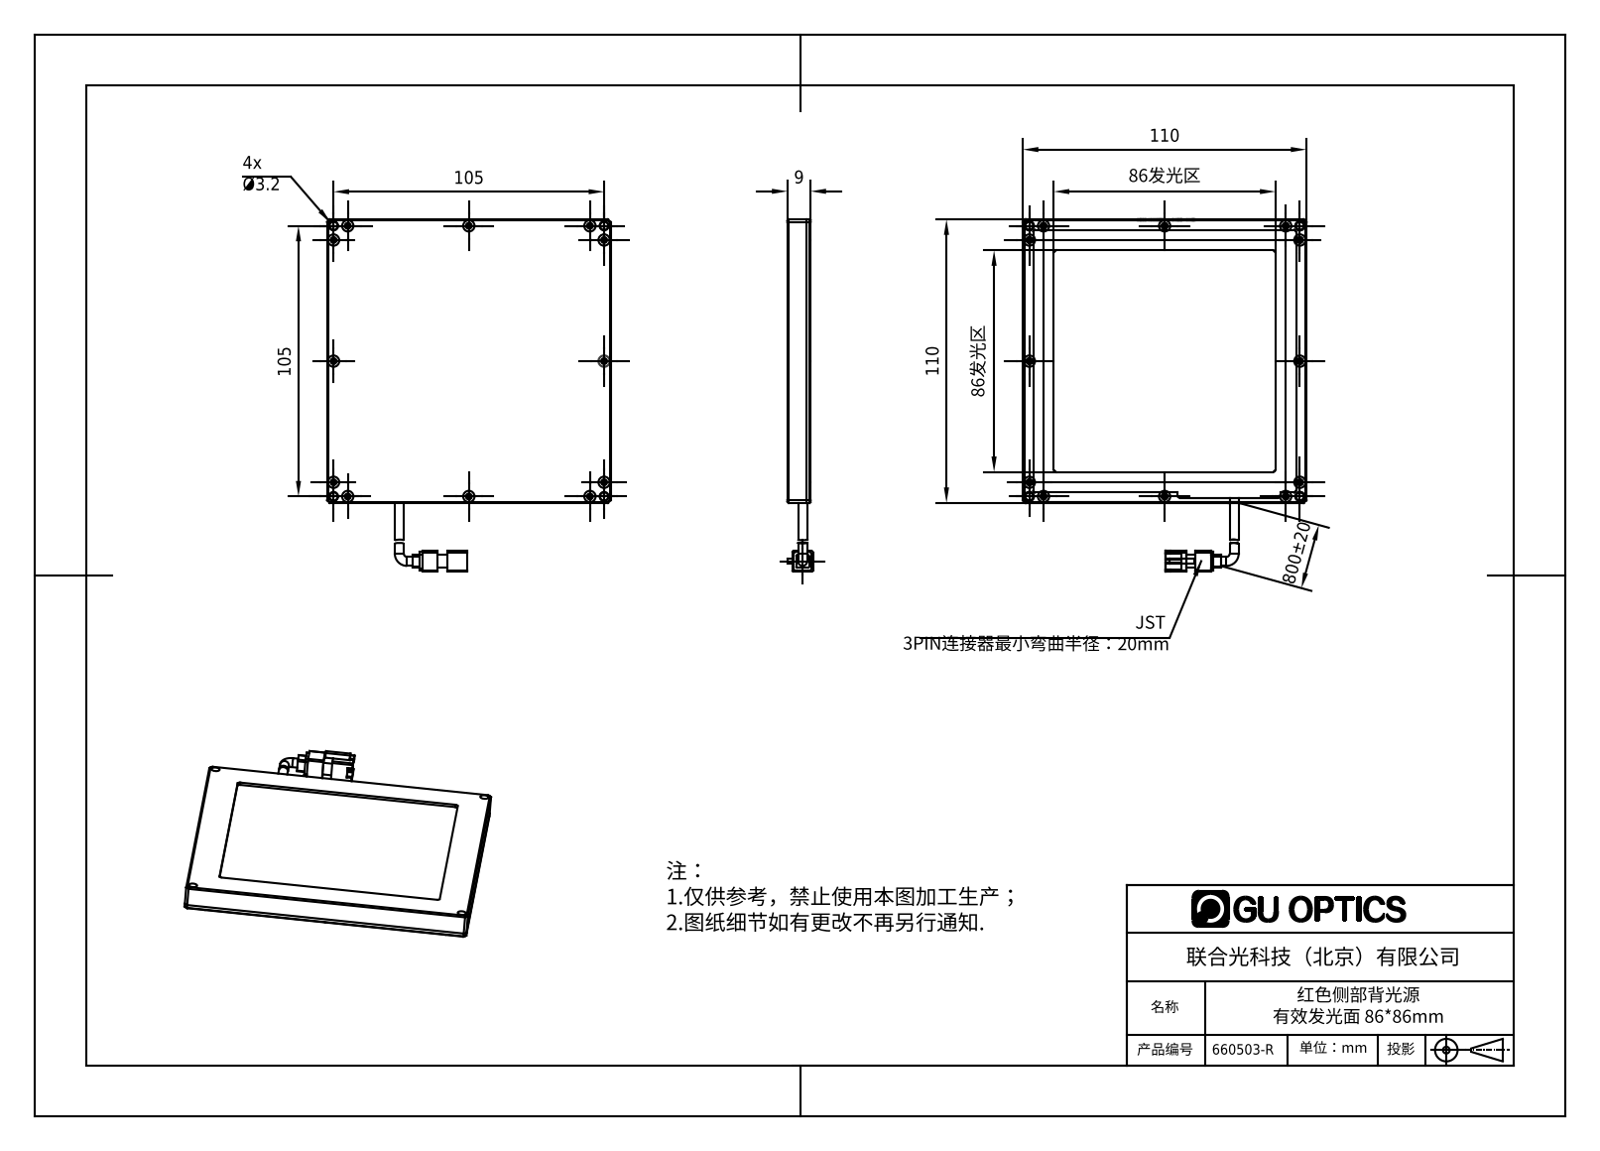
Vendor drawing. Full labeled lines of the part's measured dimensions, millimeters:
Part name (STEP PRODUCT): 660503-R
STEP written by: SolidWorks 2016 (AUTOMOTIVE_DESIGN)
Units: millimetres
Bodies: 5 solids, 415 faces (184 planar, 121 cylindrical, 110 other)
Overall size (bounding box): 136.69 × 110 × 10
Volume: 69 130 mm³ · Surface area: 61 430 mm²
Round holes (diameter × count): ⌀1.6 ×12, ⌀2 ×12, ⌀2.2 ×12, ⌀3.2 ×4, ⌀3.5 ×4
Round bosses / shafts (diameter × count): ⌀3.5 ×2
Partial cylindrical surfaces — rounded edges, fillets, slot ends (radius × count): R1 ×14, R0.5 ×8
Main face-to-face distances: 4, 8, 6.5, 1.5, 2.5, 1, 5, 9, 7.5, 102
Hole centre spacings: 105, 5.5, 47, 52.5, 52.79, 99.5, 99.65, 105.14
